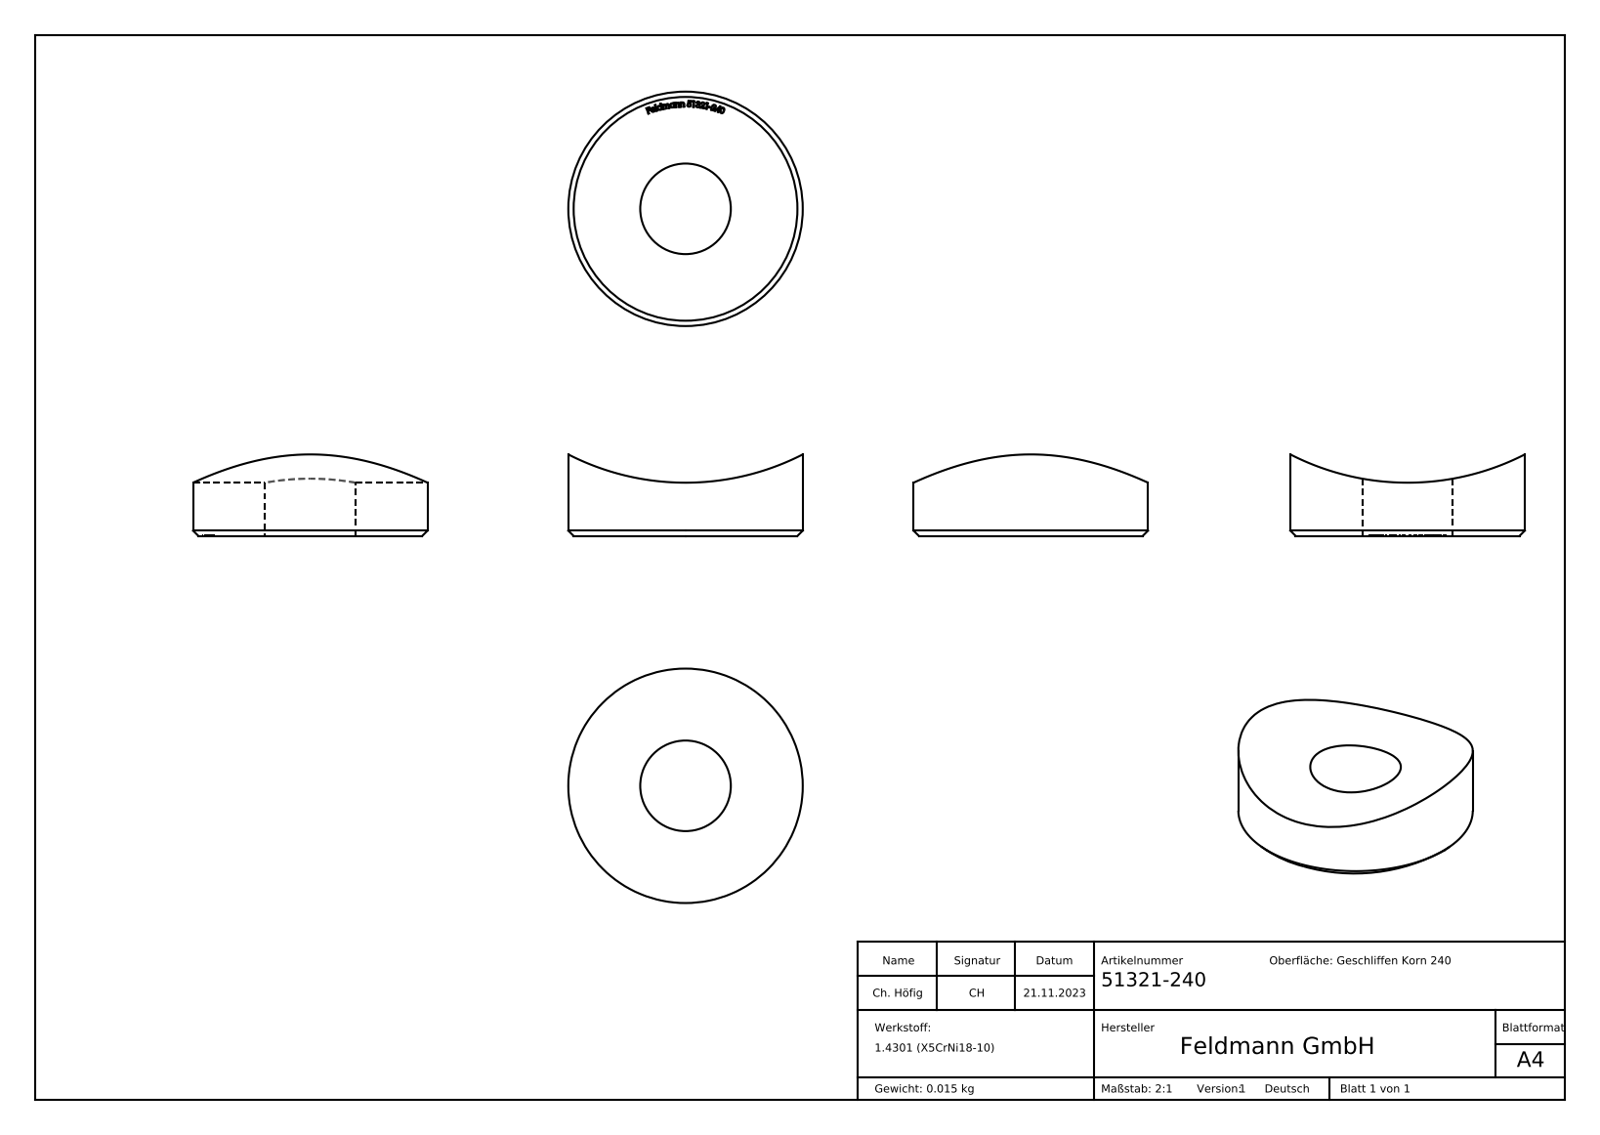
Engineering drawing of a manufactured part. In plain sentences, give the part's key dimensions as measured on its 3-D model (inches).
The part is named "51321-240". Its 3-D file was written by "SolidWorks 2018 (CONFIG_CONTROL_DESIGN)". It is 1 solid with 222 faces: 127 planar, 3 cylindrical and 92 other. Overall it measures 0.866 by 0.866 by 0.301 inches. Its volume is 0.113 cubic inches and its surface area 1.883 square inches. Round holes: 1 of diameter 0.335. Round bosses or shafts: 1 of diameter 0.866. Partial cylindrical surfaces (rounded edges, fillets, slot ends): 1 of radius 0.951. The main face-to-face distances are 0.013, 0.013, 0.021, 0.043, 0.019, 0.021, 0.023, 0.015, 0.041, 0.012.
